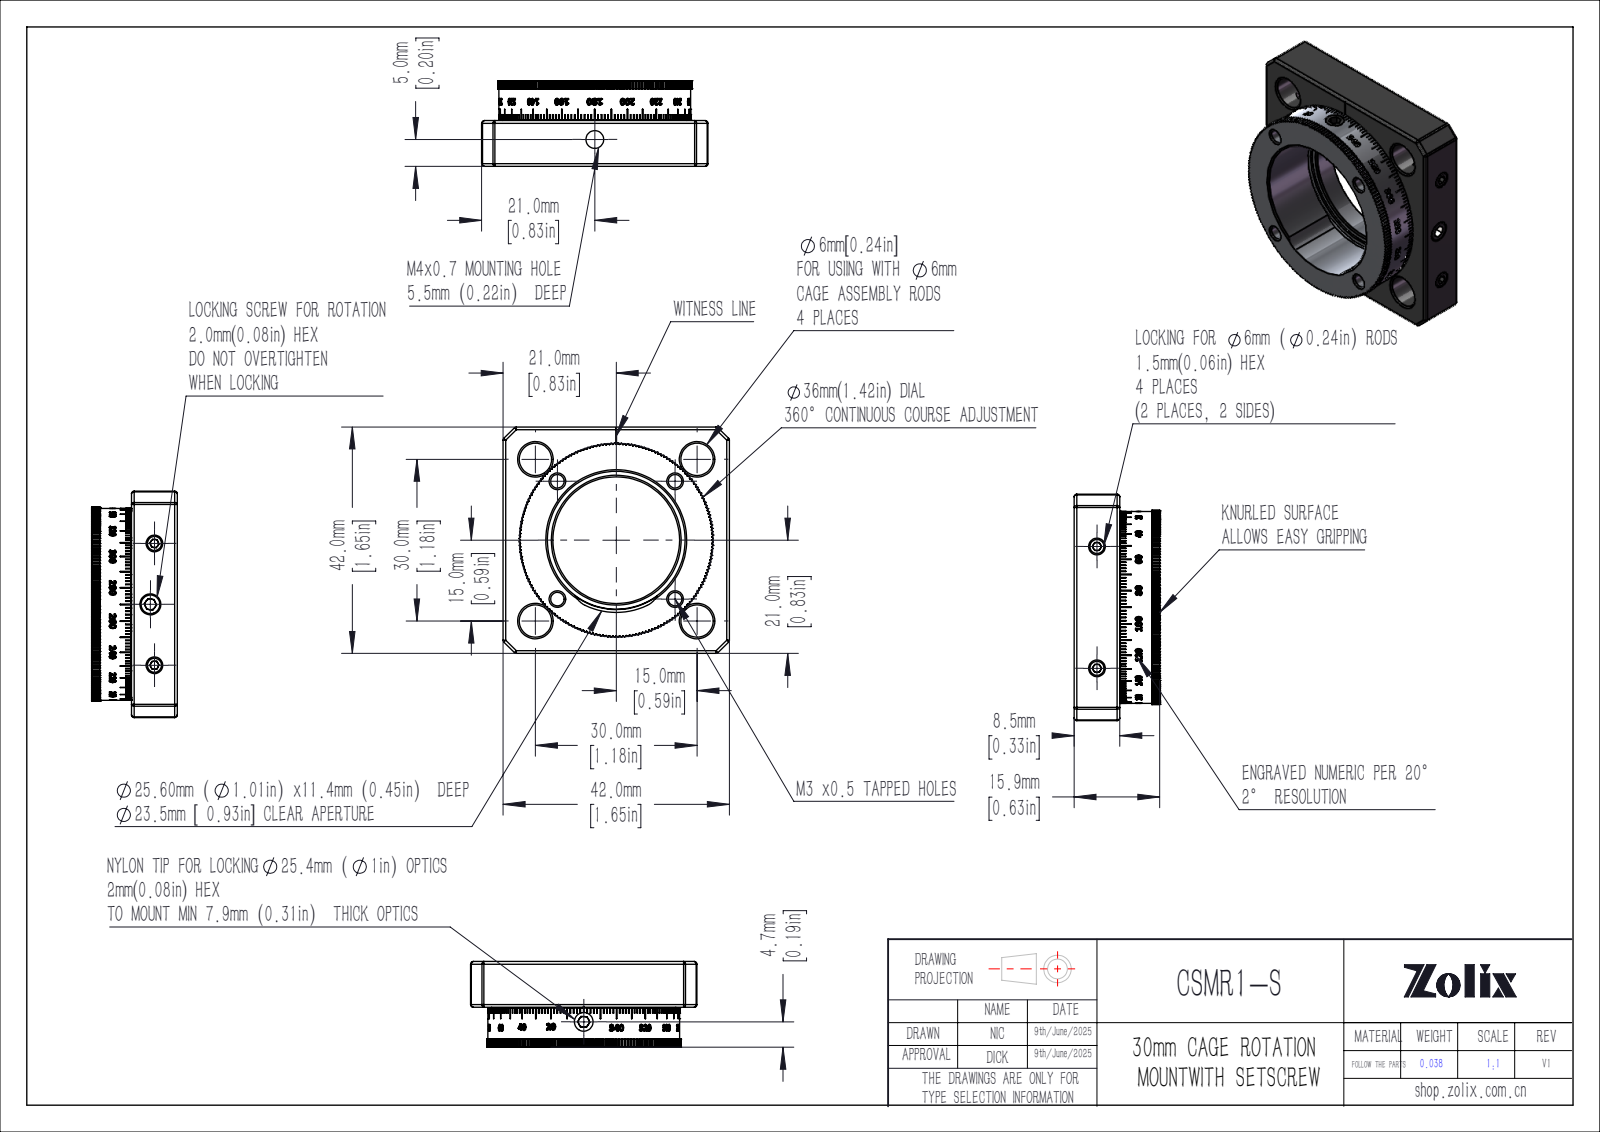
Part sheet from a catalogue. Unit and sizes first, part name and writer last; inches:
Units: inches
Overall size (bounding box): 1.654 × 1.654 × 0.622
Round holes (diameter × count): ⌀0.098 ×6, ⌀0.236 ×4, ⌀0.13 ×3, ⌀0.925 ×1, ⌀1.006 ×1, ⌀1.014 ×1, ⌀1.075 ×1, ⌀1.354 ×1
Round bosses / shafts (diameter × count): ⌀0.157 ×2, ⌀0.118 ×2, ⌀1.402 ×1, ⌀1.346 ×1, ⌀1.339 ×1, ⌀1.142 ×1, ⌀1.134 ×1, ⌀1.031 ×1
Partial cylindrical surfaces — rounded edges, fillets, slot ends (radius × count): R0.02 ×24, R0.063 ×2, R0.157 ×2, R0.528 ×1, R0.697 ×1
Main face-to-face distances: 0.335, 1.654, 0.091, 0.622, 0.287, 0.244, 0.531, 0.201, 0.197, 0.043
Hole centre spacings: 0.835, 0.86, 1.181, 0.227, 1.034, 1.443, 0.446, 0.608
Volume: 0.783 in³ · Surface area: 16.73 in²
Bodies: 9 solids, 3299 faces (1851 planar, 723 cylindrical, 725 other)
Part name (STEP PRODUCT): CSMR1-S
STEP written by: SolidWorks 2020 (CONFIG_CONTROL_DESIGN)
